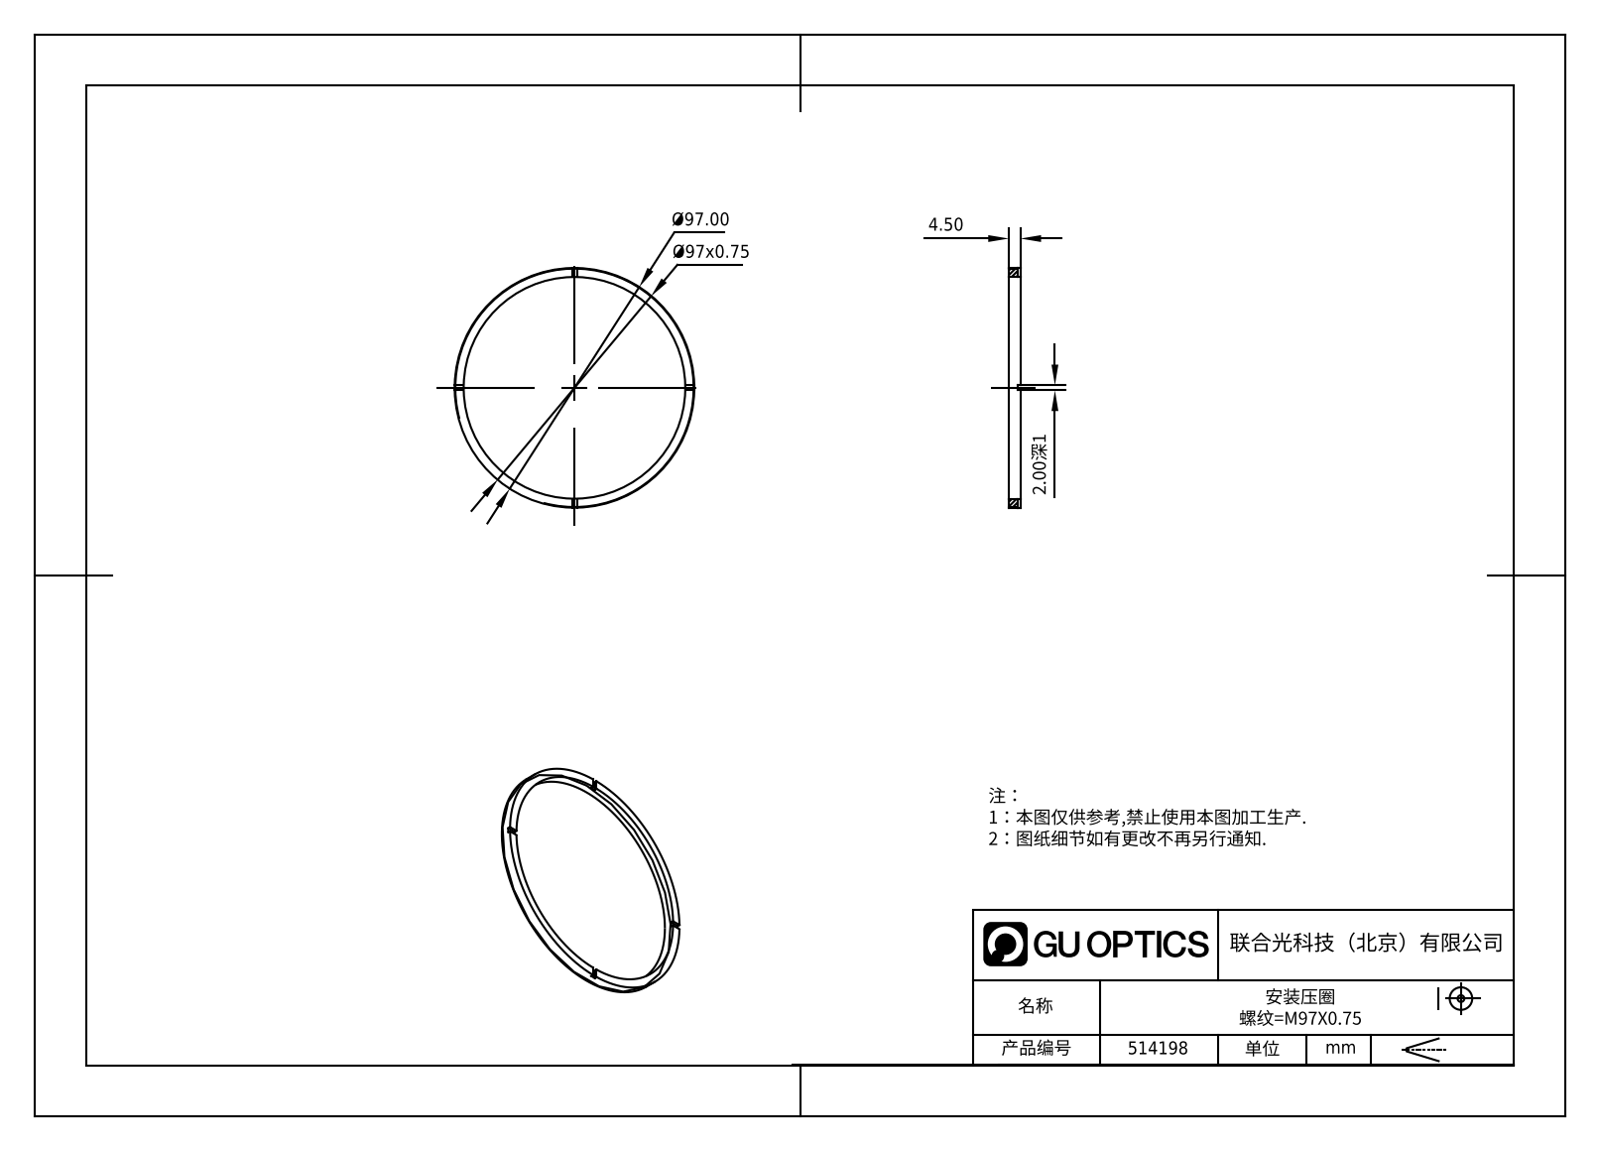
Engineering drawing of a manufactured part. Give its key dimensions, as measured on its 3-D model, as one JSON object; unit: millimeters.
{"part_name": "514198", "step_written_by": "SolidWorks 2020 (CONFIG_CONTROL_DESIGN)", "units": "millimeters", "bodies": {"solids": 1, "faces": 21, "planar": 17, "cylindrical": 4, "other": 0}, "overall_size": [97, 97, 4.5], "volume_mm3": 4598, "surface_area_mm2": 4712, "round_holes": [[90, 1]], "round_bosses_or_shafts": [[97, 1]], "face_to_face_distances": [4.5, 3.5, 1, 2]}
